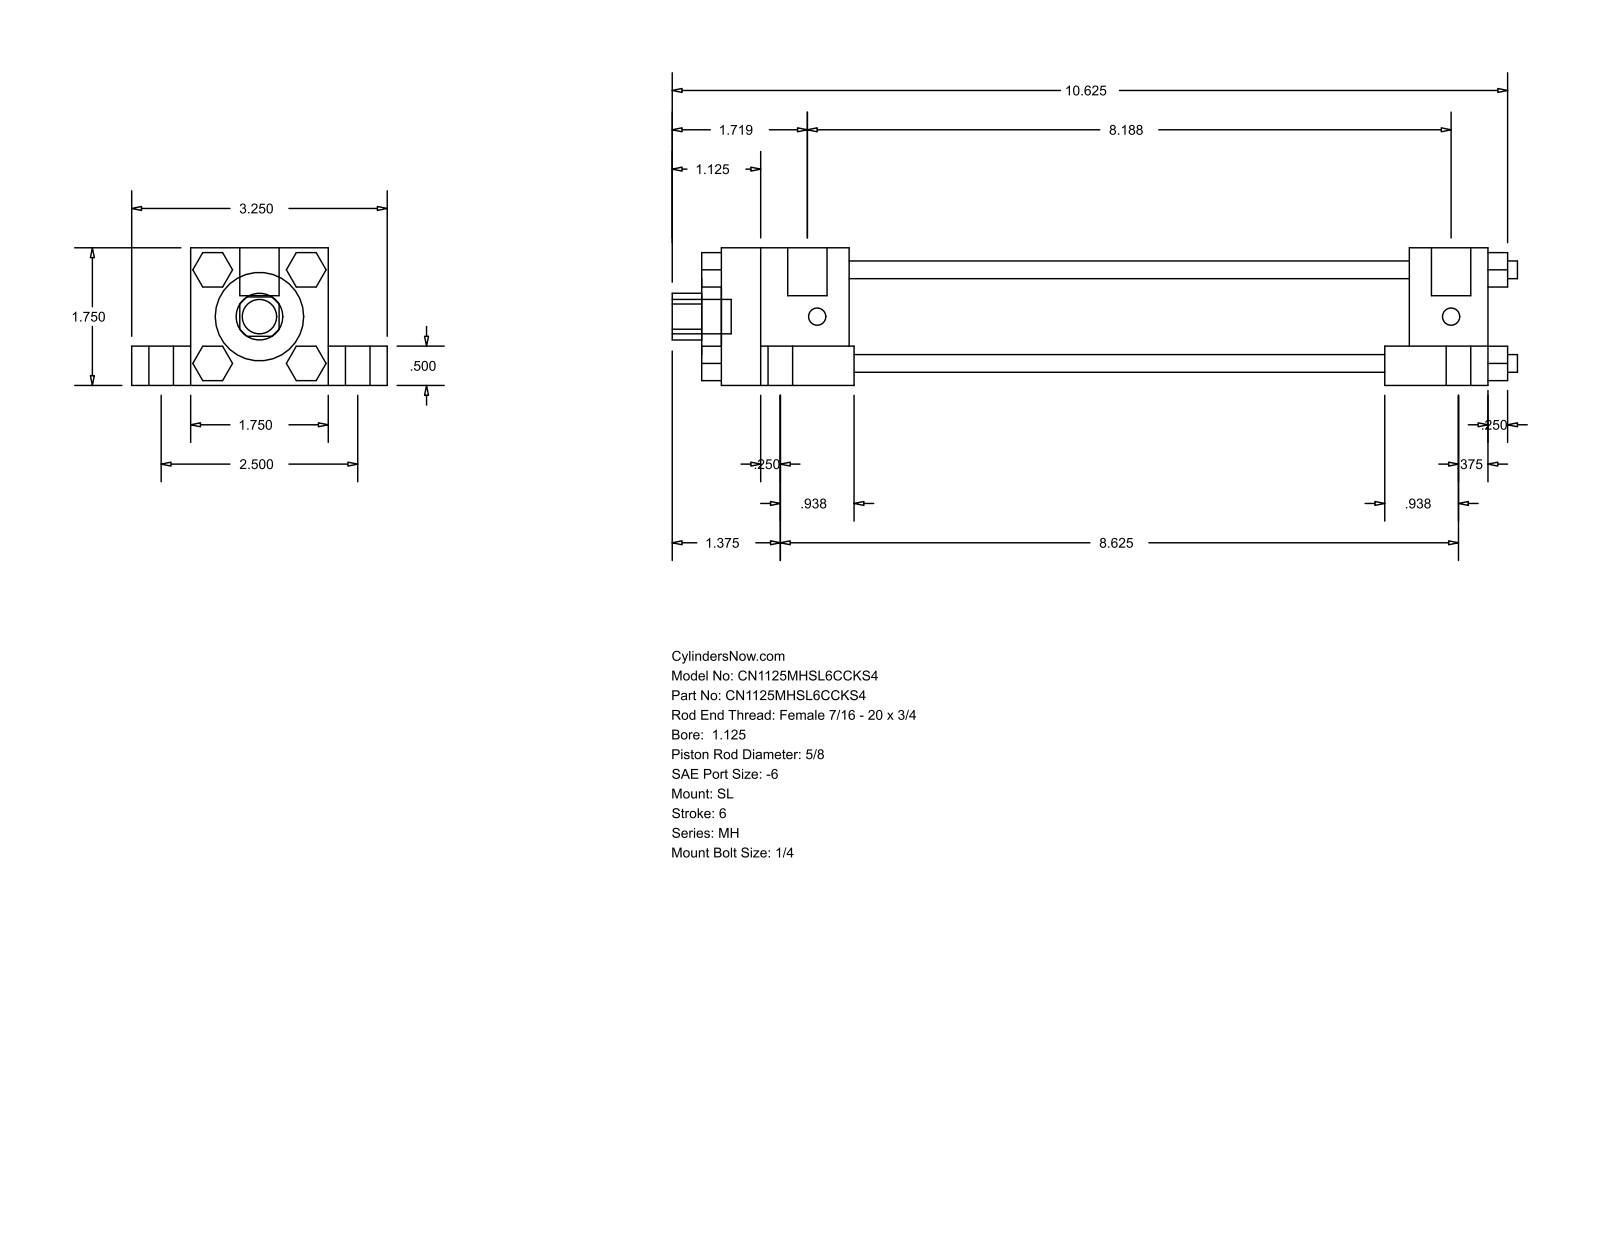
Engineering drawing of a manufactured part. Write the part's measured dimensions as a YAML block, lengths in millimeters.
part_name: "MH_SL__0112_0.625"
step_written_by: "GSSL Pune (CONFIG_CONTROL_DESIGN)"
units: millimeters
bodies: {solids: 0, faces: 150, planar: 114, cylindrical: 36, other: 0}
overall_size: [273.05, 82.55, 44.45]
round_holes:
  - {diameter: 15.88, count: 1}
  - {diameter: 28.57, count: 1}
  - {diameter: 34.92, count: 1}
round_bosses_or_shafts:
  - {diameter: 14.29, count: 4}
  - {diameter: 7.94, count: 4}
  - {diameter: 5.71, count: 4}
  - {diameter: 5.56, count: 4}
  - {diameter: 12.7, count: 2}
  - {diameter: 11.11, count: 1}
partial_cylinders:
  - {radius: 7.54, count: 1}
face_to_face_distances: [44.46, 31.76, 19.04, 12.7, 63.5, 11.11, 180.97, 206.37, 25.4, 41.27]
